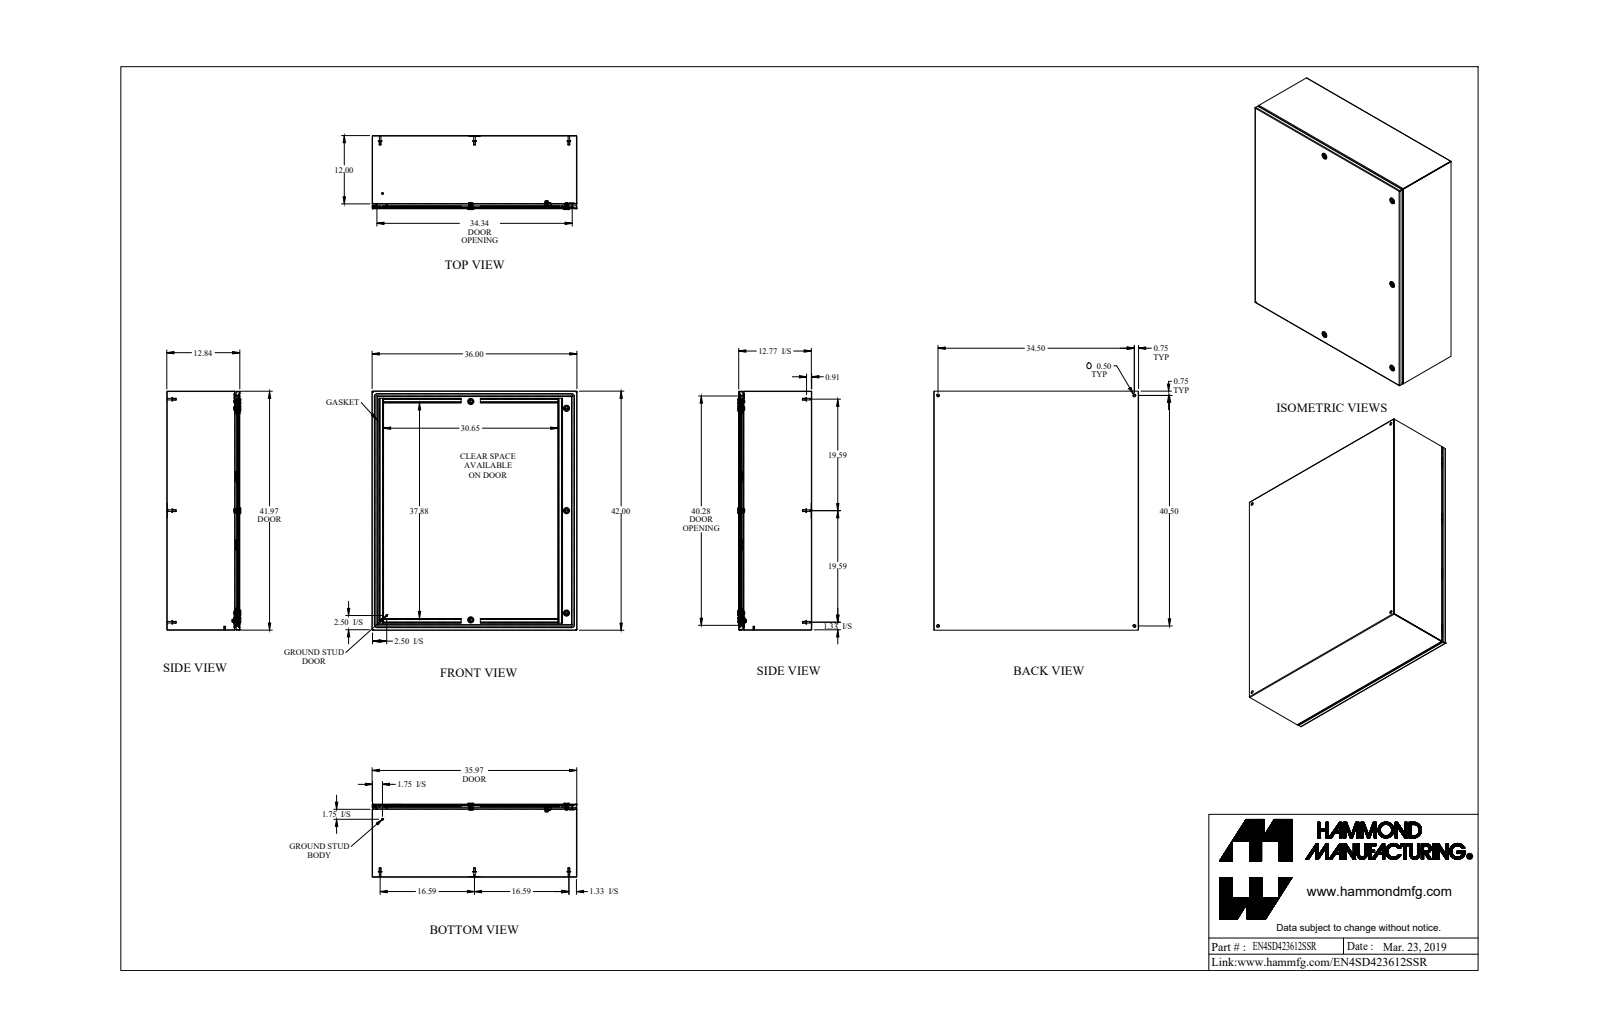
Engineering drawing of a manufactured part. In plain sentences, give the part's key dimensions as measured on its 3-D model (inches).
The part is named "EN4SD423612SSR". Its 3-D file was written by "SolidWorks 2018 (AUTOMOTIVE_DESIGN)". It is 66 solids with 1714 faces: 896 planar, 545 cylindrical and 273 other. Overall it measures 42 by 36 by 13.002 inches. Its volume is 403.3 cubic inches and its surface area 11 369 square inches. Round holes: 9 of diameter 0.5, 5 of diameter 0.197, 5 of diameter 0.387, 5 of diameter 0.63, 5 of diameter 0.768, 1 of diameter 0.172, 1 of diameter 0.196, 1 of diameter 0.24, 1 of diameter 0.242, 1 of diameter 0.275, 1 of diameter 0.375. Round bosses or shafts: 12 of diameter 0.625, 10 of diameter 0.313, 8 of diameter 0.275, 5 of diameter 1.1, 5 of diameter 0.785, 5 of diameter 0.525, 5 of diameter 0.236, 2 of diameter 0.625. Partial cylindrical surfaces (rounded edges, fillets, slot ends): 32 of radius 0.048, 24 of radius 0.01, 18 of radius 0.036, 18 of radius 0.108, 14 of radius 0.062, 10 of radius 0.094, 10 of radius 0.125, 9 of radius 0.016. The main face-to-face distances are 0.072, 12.77, 12.698, 12.842, 35.928, 41.928, 35.856, 36, 41.856, 42. The hole center spacings are 16.622, 16.881, 17.943, 20.278, 25.529, 33.504, 34.5, 39.082.
